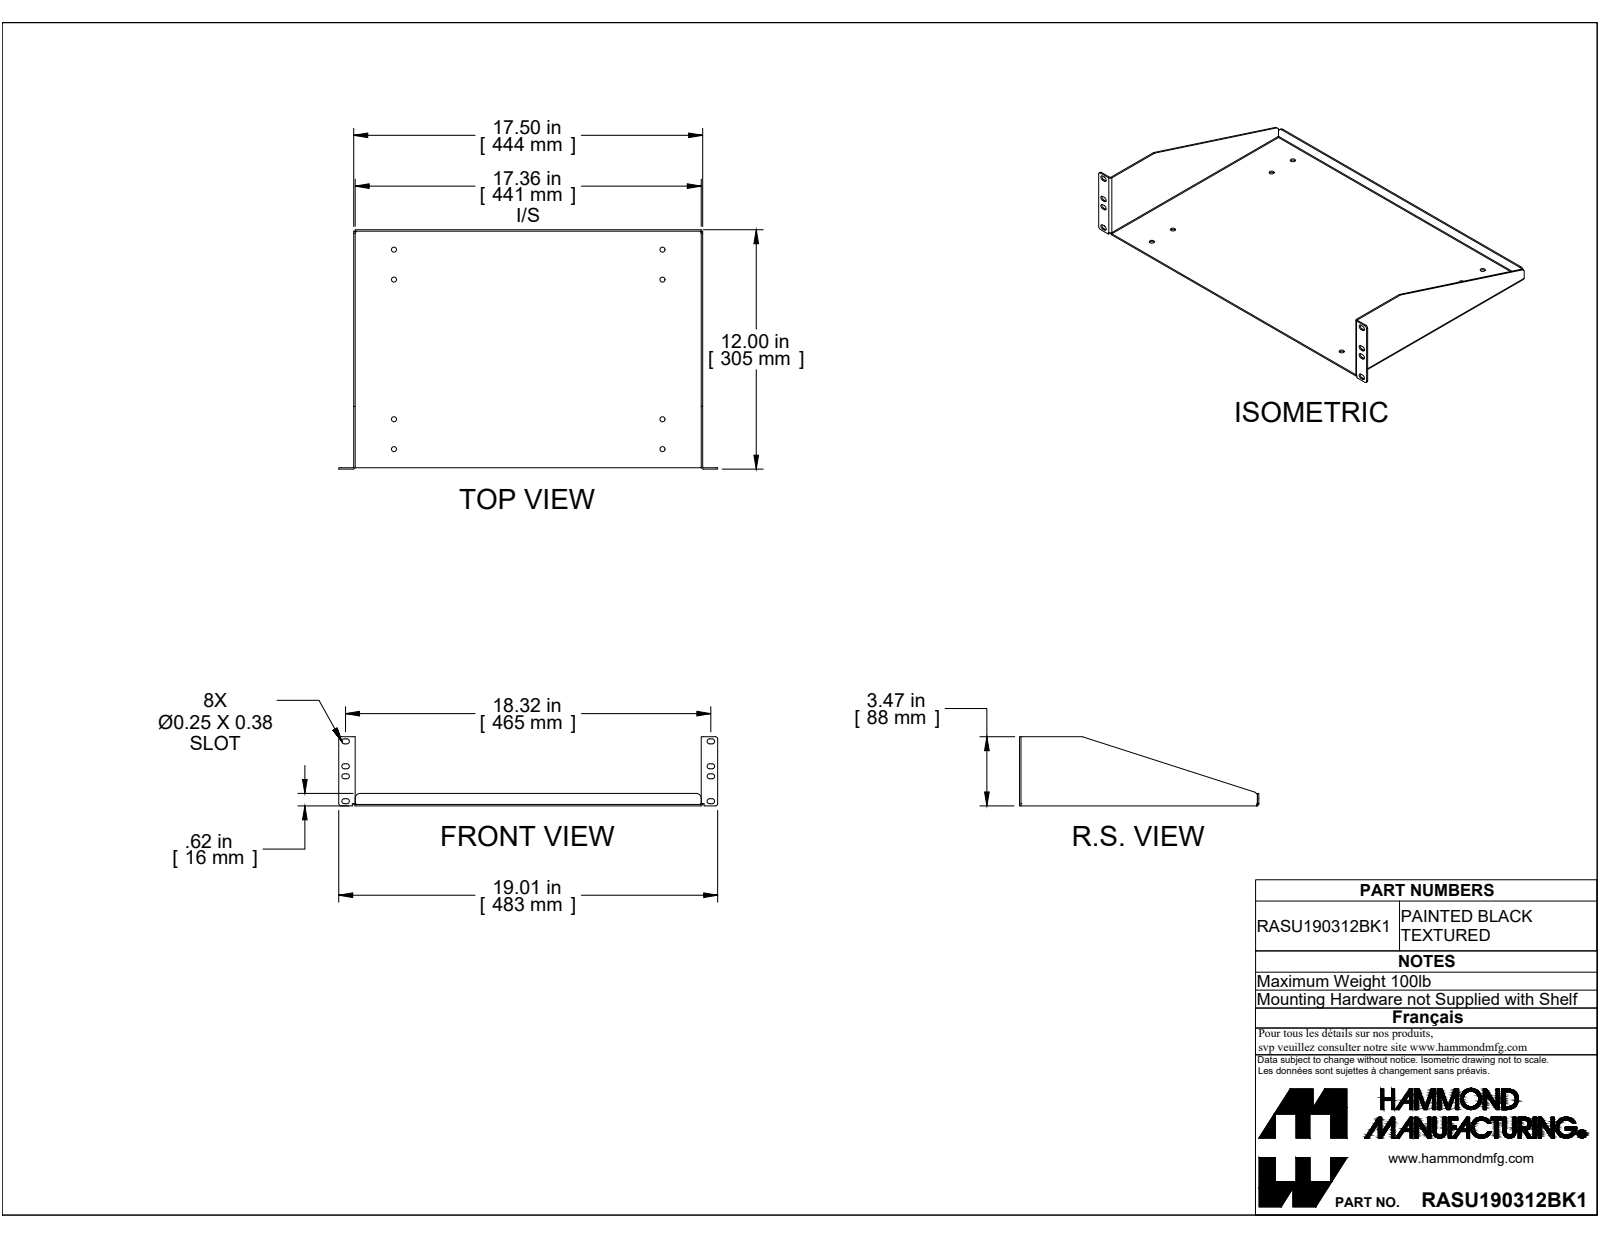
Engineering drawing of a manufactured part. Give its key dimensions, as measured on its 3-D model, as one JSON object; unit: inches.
{"part_name": "RASU190312BK1", "step_written_by": "SolidWorks 2019 (CONFIG_CONTROL_DESIGN)", "units": "inches", "bodies": {"solids": 1, "faces": 104, "planar": 56, "cylindrical": 44, "other": 4}, "overall_size": [19.006, 12, 3.468], "volume_in3": 19.96, "surface_area_in2": 560.7, "round_holes": [[0.25, 8]], "partial_cylinders_radius": [[0.125, 20], [0.036, 5], [0.108, 5], [0.055, 3], [0.25, 2]], "face_to_face_distances": [0.072, 17.428, 17.356, 17.5, 11.856, 11.928, 0.072, 11.928, 12, 0.625], "hole_center_spacings": [1.5, 8.5, 13.468, 13.551, 15.926, 7, 10, 15.178]}
